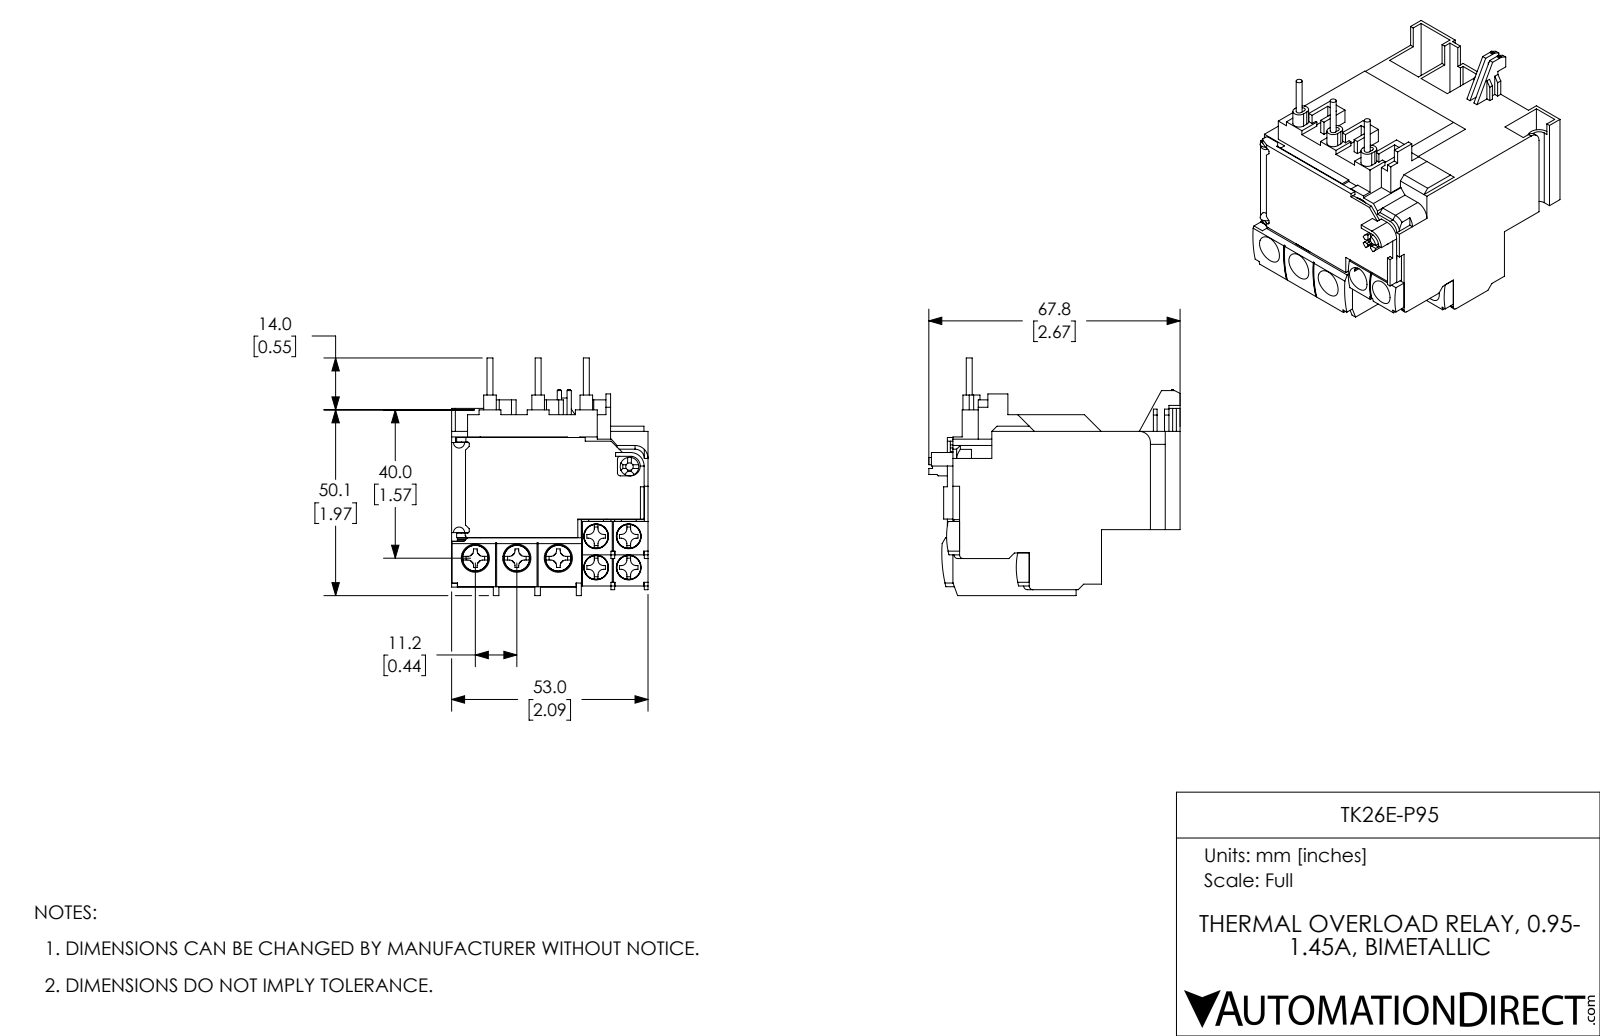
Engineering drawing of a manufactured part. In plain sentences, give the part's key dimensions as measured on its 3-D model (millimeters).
The part is named "TK26E-P95". Its 3-D file was written by "SolidWorks 2017 (AUTOMOTIVE_DESIGN)". It is 38 solids with 1480 faces: 1225 planar, 220 cylindrical and 35 other. Overall it measures 67.8 by 64.1 by 53 millimeters. Its volume is 99 940 cubic millimeters and its surface area 38 810 square millimeters. Round holes: 4 of diameter 3.5, 4 of diameter 3.6, 4 of diameter 6.7, 3 of diameter 4, 3 of diameter 4.1, 3 of diameter 7.6, 1 of diameter 1, 1 of diameter 2, 1 of diameter 5, 1 of diameter 11. Round bosses or shafts: 4 of diameter 6.6, 3 of diameter 1.6, 1 of diameter 6. Partial cylindrical surfaces (rounded edges, fillets, slot ends): 28 of radius 1.5, 8 of radius 1, 6 of radius 0.5, 6 of radius 1.7, 5 of radius 0.8, 4 of radius 1.2, 4 of radius 4.3, 3 of radius 4.8. The main face-to-face distances are 1, 9, 1.5, 12, 53, 2, 10, 11, 8.7, 0.7. The hole center spacings are 8.4, 8.8, 11.2, 12.2, 9.6, 10.5, 11.8, 18.8.
